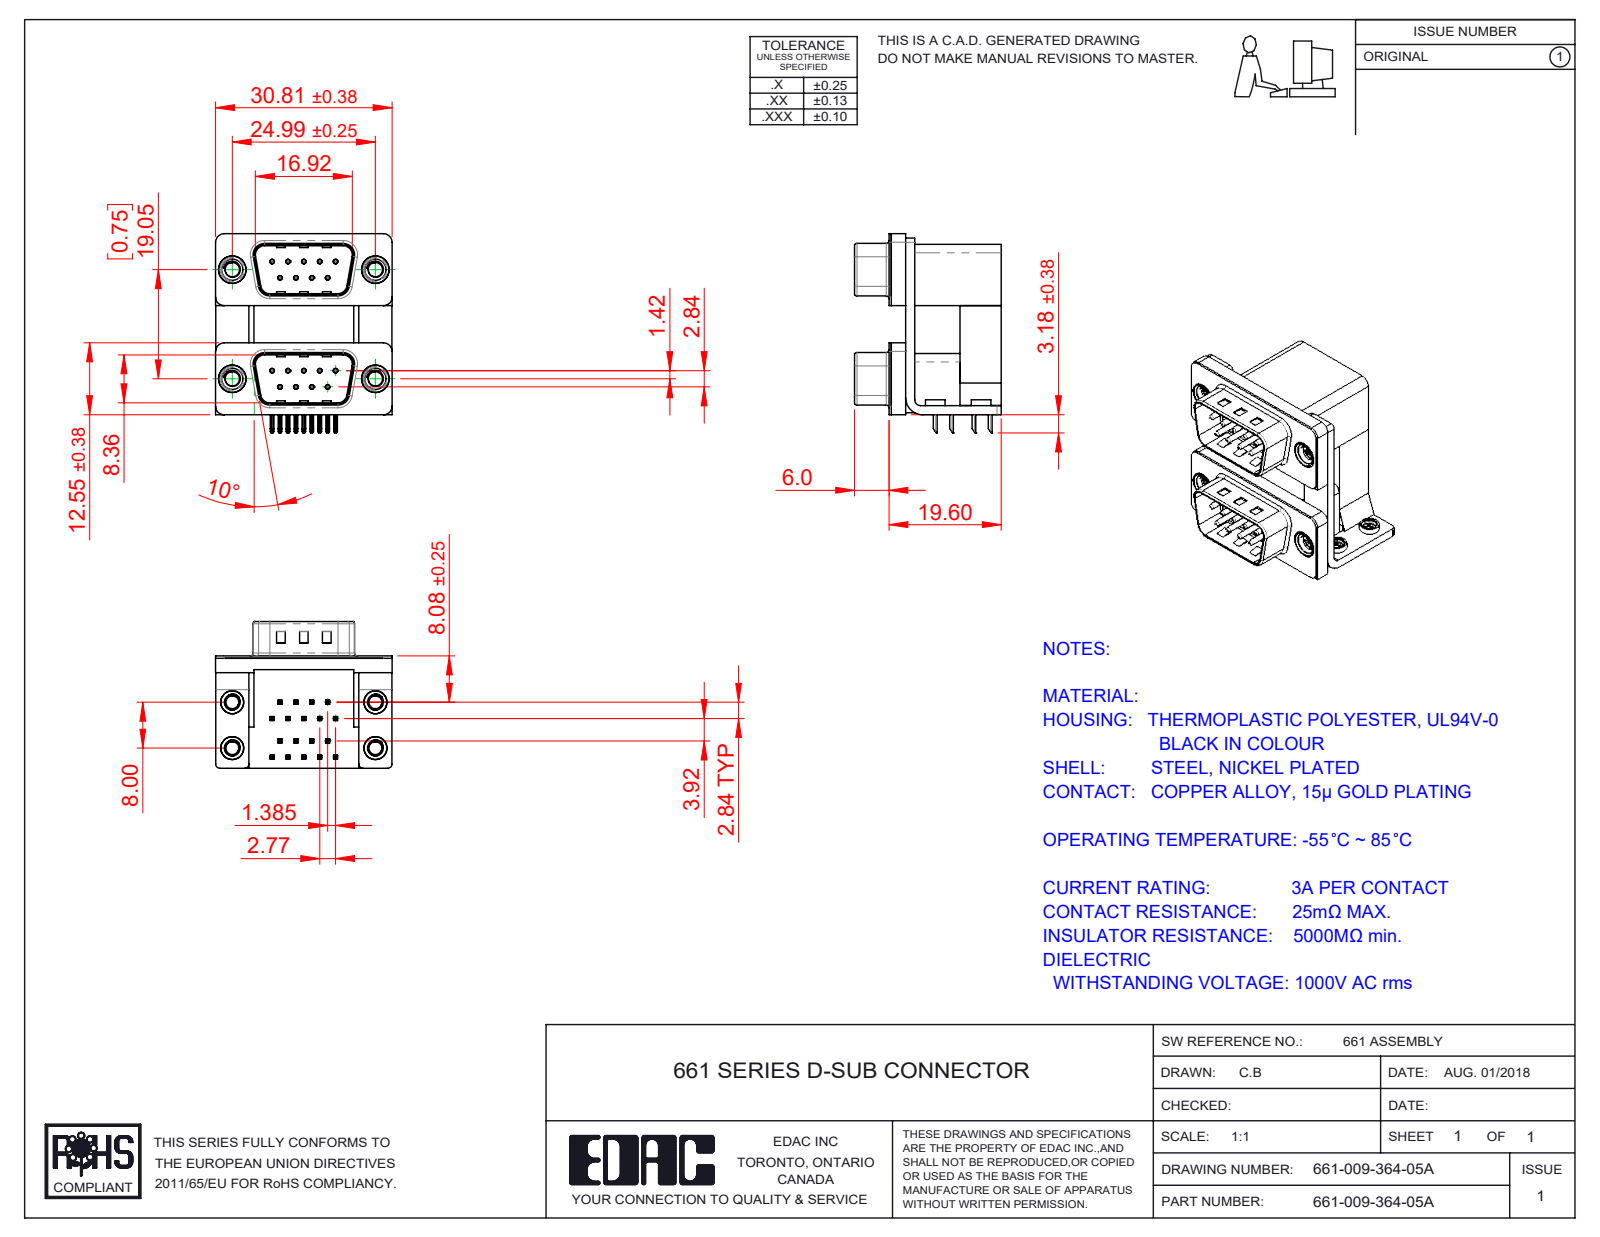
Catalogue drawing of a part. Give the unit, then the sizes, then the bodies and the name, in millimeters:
Units: millimetres
Overall size (bounding box): 34.78 × 30.81 × 25.6
Round holes (diameter × count): ⌀0.35 ×18, ⌀0.8 ×18, ⌀2.26 ×4, ⌀2.5 ×4, ⌀2.75 ×4, ⌀3.2 ×4, ⌀3.5 ×4, ⌀4 ×4, ⌀4.8 ×4, ⌀5 ×4
Round bosses / shafts (diameter × count): ⌀0.75 ×18, ⌀4.9 ×4, ⌀4.75 ×4, ⌀4 ×4, ⌀3.9 ×4, ⌀3.4 ×4
Partial cylindrical surfaces — rounded edges, fillets, slot ends (radius × count): R0.25 ×72, R0.12 ×36, R0.5 ×16, R1.5 ×14, R0.75 ×8, R0.9 ×8, R1.6 ×8, R2 ×8
Main face-to-face distances: 0.4, 2.5, 19.05, 16.7, 19.2, 10.69, 7.2, 9.5, 12, 1.6
Hole centre spacings: 3.16, 2.77, 19.25, 19.05, 5.54, 19.84, 16.27, 21.93
Volume: 10 311 mm³ · Surface area: 12 085 mm²
Bodies: 33 solids, 2092 faces (1164 planar, 678 cylindrical, 250 other)
Part name (STEP PRODUCT): 661 Contact Top Lower; 661-009-364-05A; 661 Threaded Rivet_M3; 661 Housing Lower_09 Contacts (+8 more)
STEP written by: SolidWorks 2020 (CONFIG_CONTROL_DESIGN)
